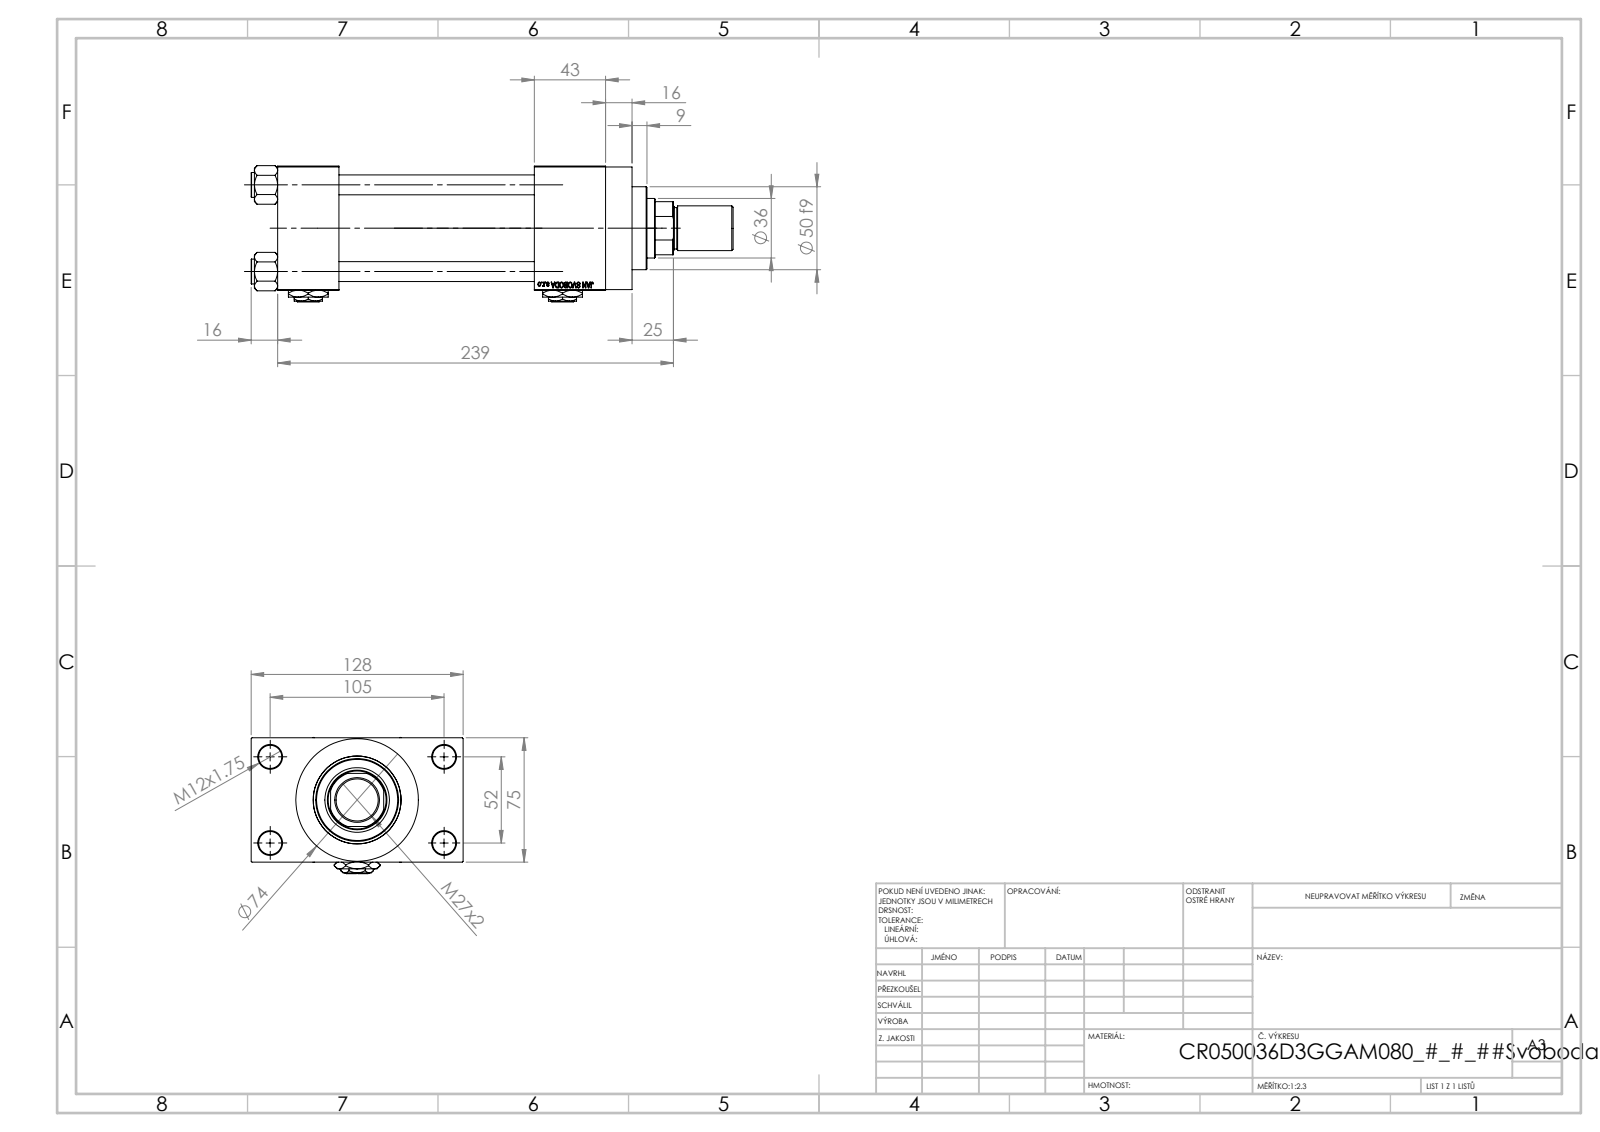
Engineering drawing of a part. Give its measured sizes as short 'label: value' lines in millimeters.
name: V215CR_VCP_D; Zatka_pro_OIL_PORT; ROD_END_AH; NUT_M5_D (+3 more)
written by: SolidWorks 2019 (CONFIG_CONTROL_DESIGN)
unit: mm
bodies: 14 solids, 1219 faces (549 planar, 104 cylindrical, 566 other)
size: 291 × 128 × 82.27
volume: 960 574 mm³; area: 218 109 mm²
holes: 4× ⌀12, 4× ⌀14, 2× ⌀7, 2× ⌀20.96, 2× ⌀30, 1× ⌀25.5, 1× ⌀36, 1× ⌀39, 1× ⌀41, 1× ⌀53
bosses: 4× ⌀15, 1× ⌀74, 1× ⌀56, 1× ⌀50, 1× ⌀27, 1× ⌀25
rounds: 1× R17.5
face distances: 75, 118, 37, 155, 26.5, 101.5, 198, 43, 161, 16
hole spacings: 26.35, 36.98, 52.3, 58.43, 58.59, 78.65, 94.37, 52
